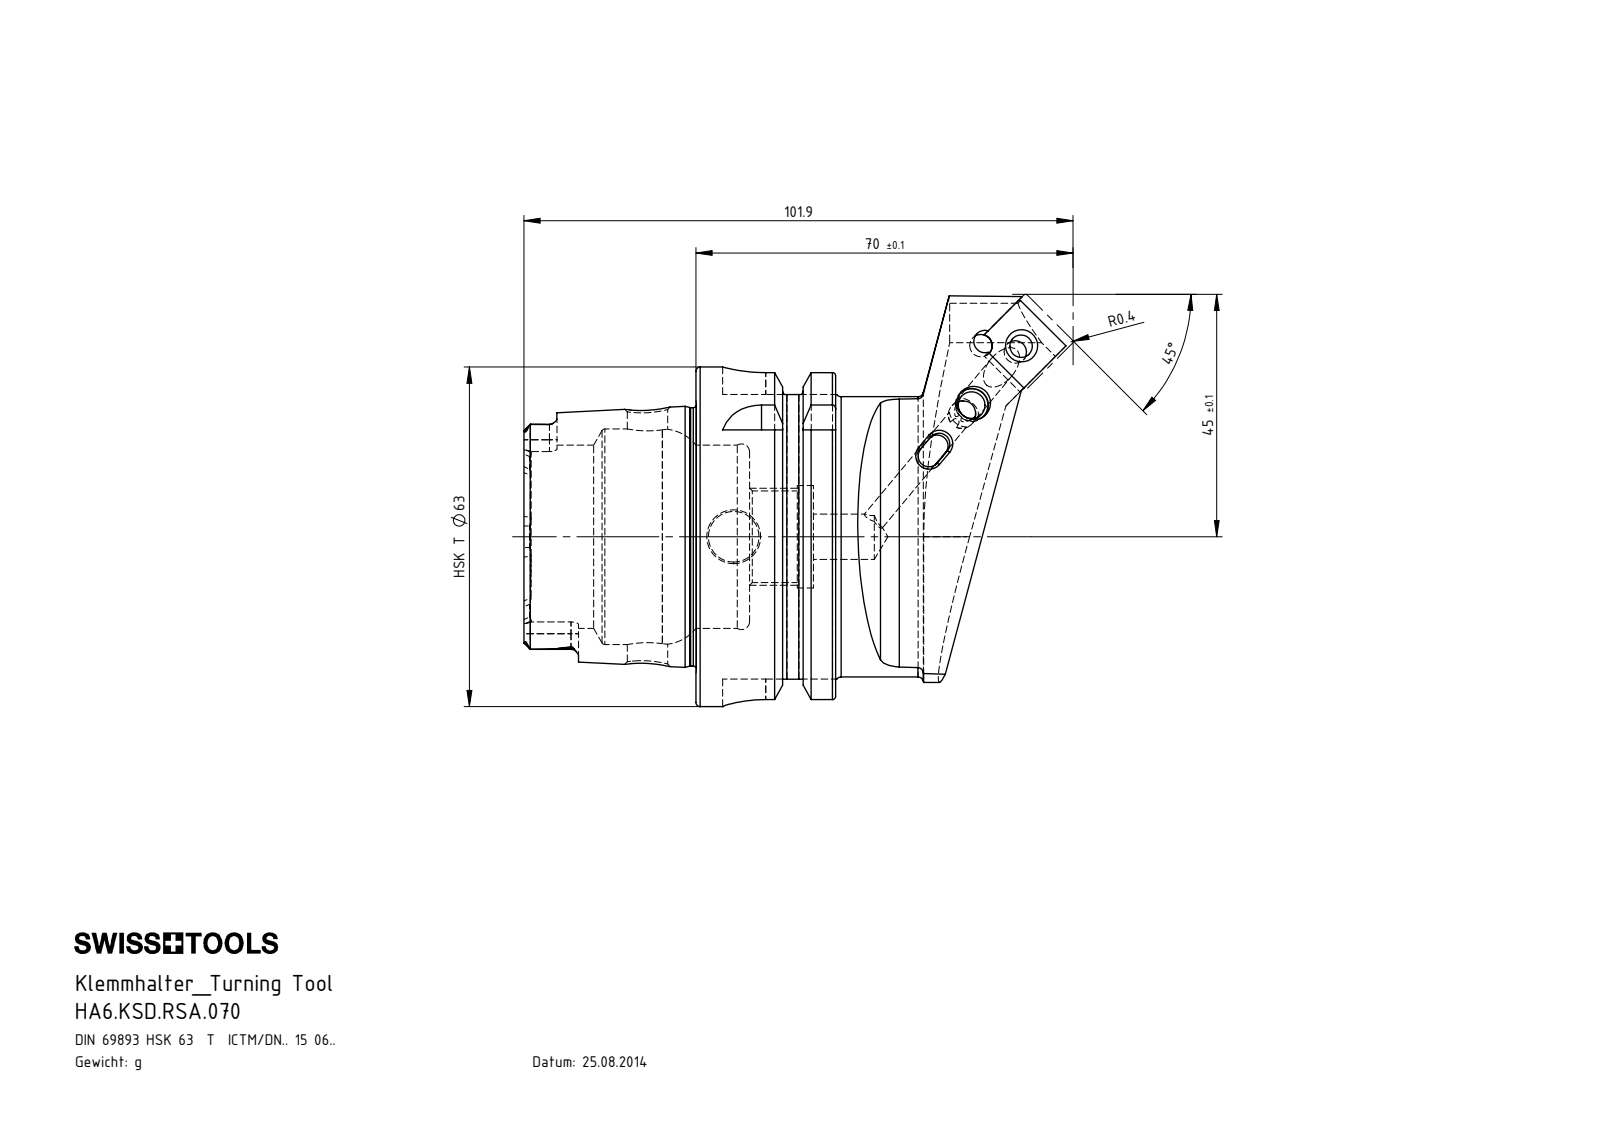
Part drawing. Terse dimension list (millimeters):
name: WCC-ER2.001.010_A; ISO 13337 - 3 x 12_PreviewCfg; WCC-ER3.102.024_C; WCC-ER4.103.032_A (+6 more)
written by: SolidWorks 2022 (CONFIG_CONTROL_DESIGN)
unit: mm
bodies: 10 solids, 477 faces (124 planar, 152 cylindrical, 201 other)
size: 101.9 × 76.5 × 63
volume: 134 876 mm³; area: 34 669 mm²
holes: 3× ⌀2, 3× ⌀5, 2× ⌀4.2, 2× ⌀6.2, 2× ⌀7, 1× ⌀2.4, 1× ⌀3, 1× ⌀5.16, 1× ⌀6, 1× ⌀6.5, 1× ⌀7.5, 1× ⌀8.4
bosses: 2× ⌀6, 2× ⌀3, 1× ⌀63, 1× ⌀54.95, 1× ⌀52, 1× ⌀47.94, 1× ⌀14, 1× ⌀11.5
rounds: 6× R0.39, 6× R0.69, 6× R1.4, 4× R0.4, 4× R2.88, 4× R8, 3× R0.8, 3× R1.5
face distances: 25.95, 16, 9.95, 31.9, 41.85, 57.85, 52.8, 21.8, 11.85, 12.19
hole spacings: 8.2, 14.8, 7.57, 8, 15, 15.01, 17.85, 23
